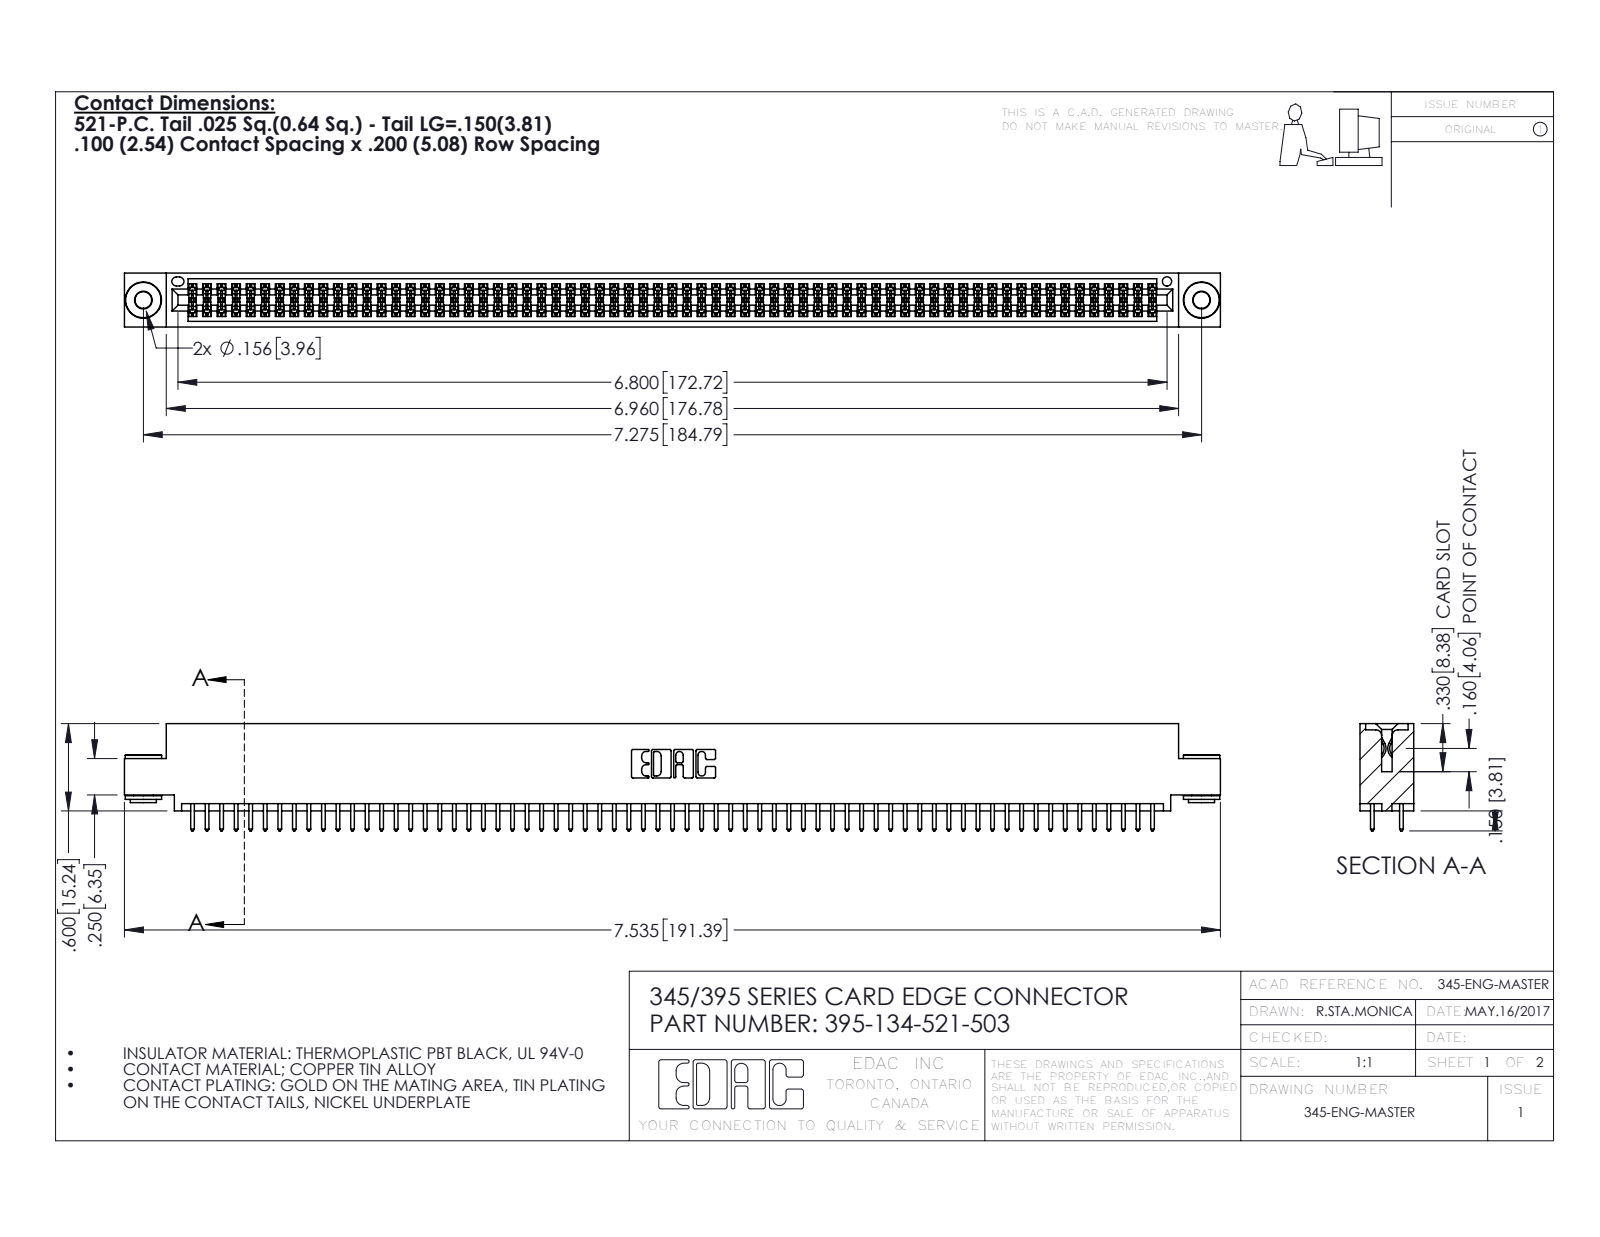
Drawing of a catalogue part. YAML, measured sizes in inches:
part_name: "395-134-521-503; 345-292-001_345-293-121; 345 Part_0.110 Offset - 0.156 Dia-TH; 345-250-002_345-250-002-102"
step_written_by: "SolidWorks 2016 (CONFIG_CONTROL_DESIGN)"
units: inches
bodies: {solids: 137, faces: 6868, planar: 4516, cylindrical: 2344, other: 8}
overall_size: [7.535, 0.737, 0.37]
volume: 1.142
surface_area: 43.54
round_holes:
  - {diameter: 0.116, count: 2}
  - {diameter: 0.156, count: 2}
  - {diameter: 0.064, count: 1}
round_bosses_or_shafts:
  - {diameter: 0.25, count: 2}
  - {diameter: 0.18, count: 2}
  - {diameter: 0.136, count: 2}
partial_cylinders:
  - {radius: 0.006, count: 201}
  - {radius: 0.01, count: 134}
  - {radius: 0.01, count: 22}
  - {radius: 0.007, count: 6}
  - {radius: 0.031, count: 6}
  - {radius: 0.026, count: 3}
  - {radius: 0.014, count: 2}
  - {radius: 0.019, count: 2}
face_to_face_distances: [0.072, 0.298, 0.2, 0.025, 0.098, 0.272, 0.37, 0.225, 0.175, 0.149]
hole_center_spacings: [0.27, 7.039, 7.275]
